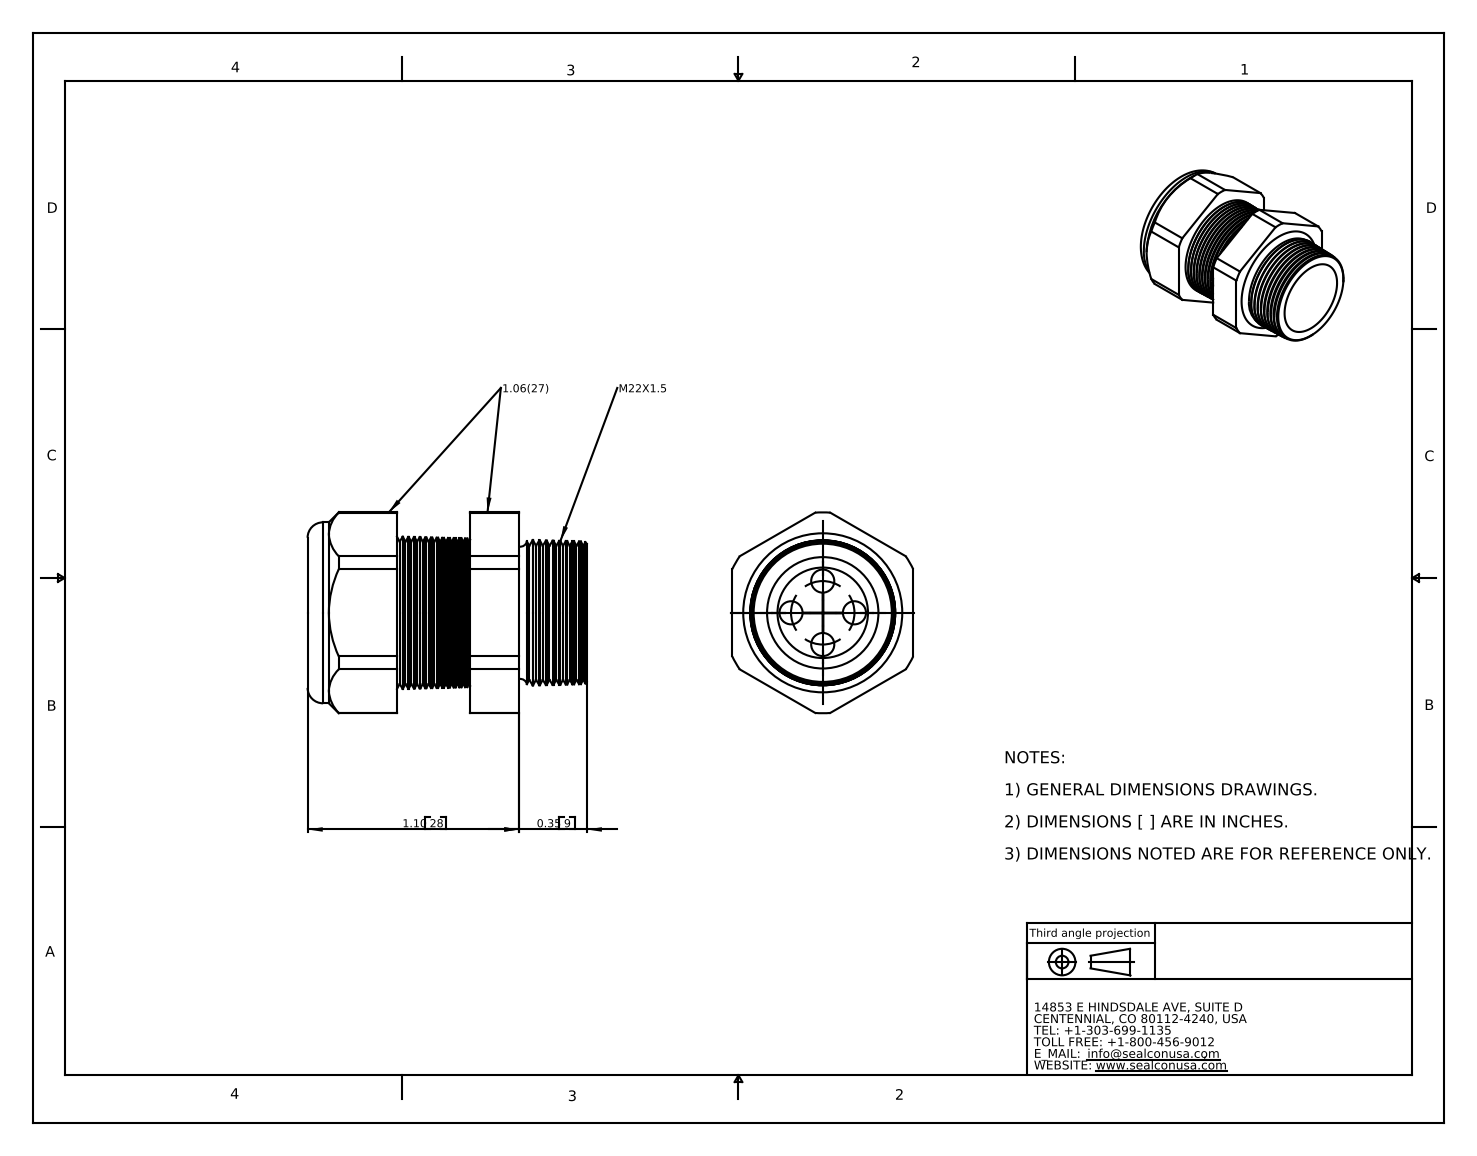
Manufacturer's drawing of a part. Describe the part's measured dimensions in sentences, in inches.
The part is named "CD22M9-BK". Its 3-D file was written by "SolidWorks 2007 (CONFIG_CONTROL_DESIGN)". It is 2 solids with 194 faces: 20 planar, 28 cylindrical and 146 other. Overall it measures 1.45 by 1.043 by 0.94 inches. Its volume is 0.584 cubic inches and its surface area 10.28 square inches. Round holes: 4 of diameter 0.12, 1 of diameter 0.45, 1 of diameter 0.47. Round bosses or shafts: 1 of diameter 0.94. Partial cylindrical surfaces (rounded edges, fillets, slot ends): 1 of radius 0.522. The main face-to-face distances are 0.94, 0.844, 0.465, 0.38, 1.1, 0.635, 0.256, 1.45, 0.985, 0.606. The hole center spacings are 0.165, 0.233, 0.329.
